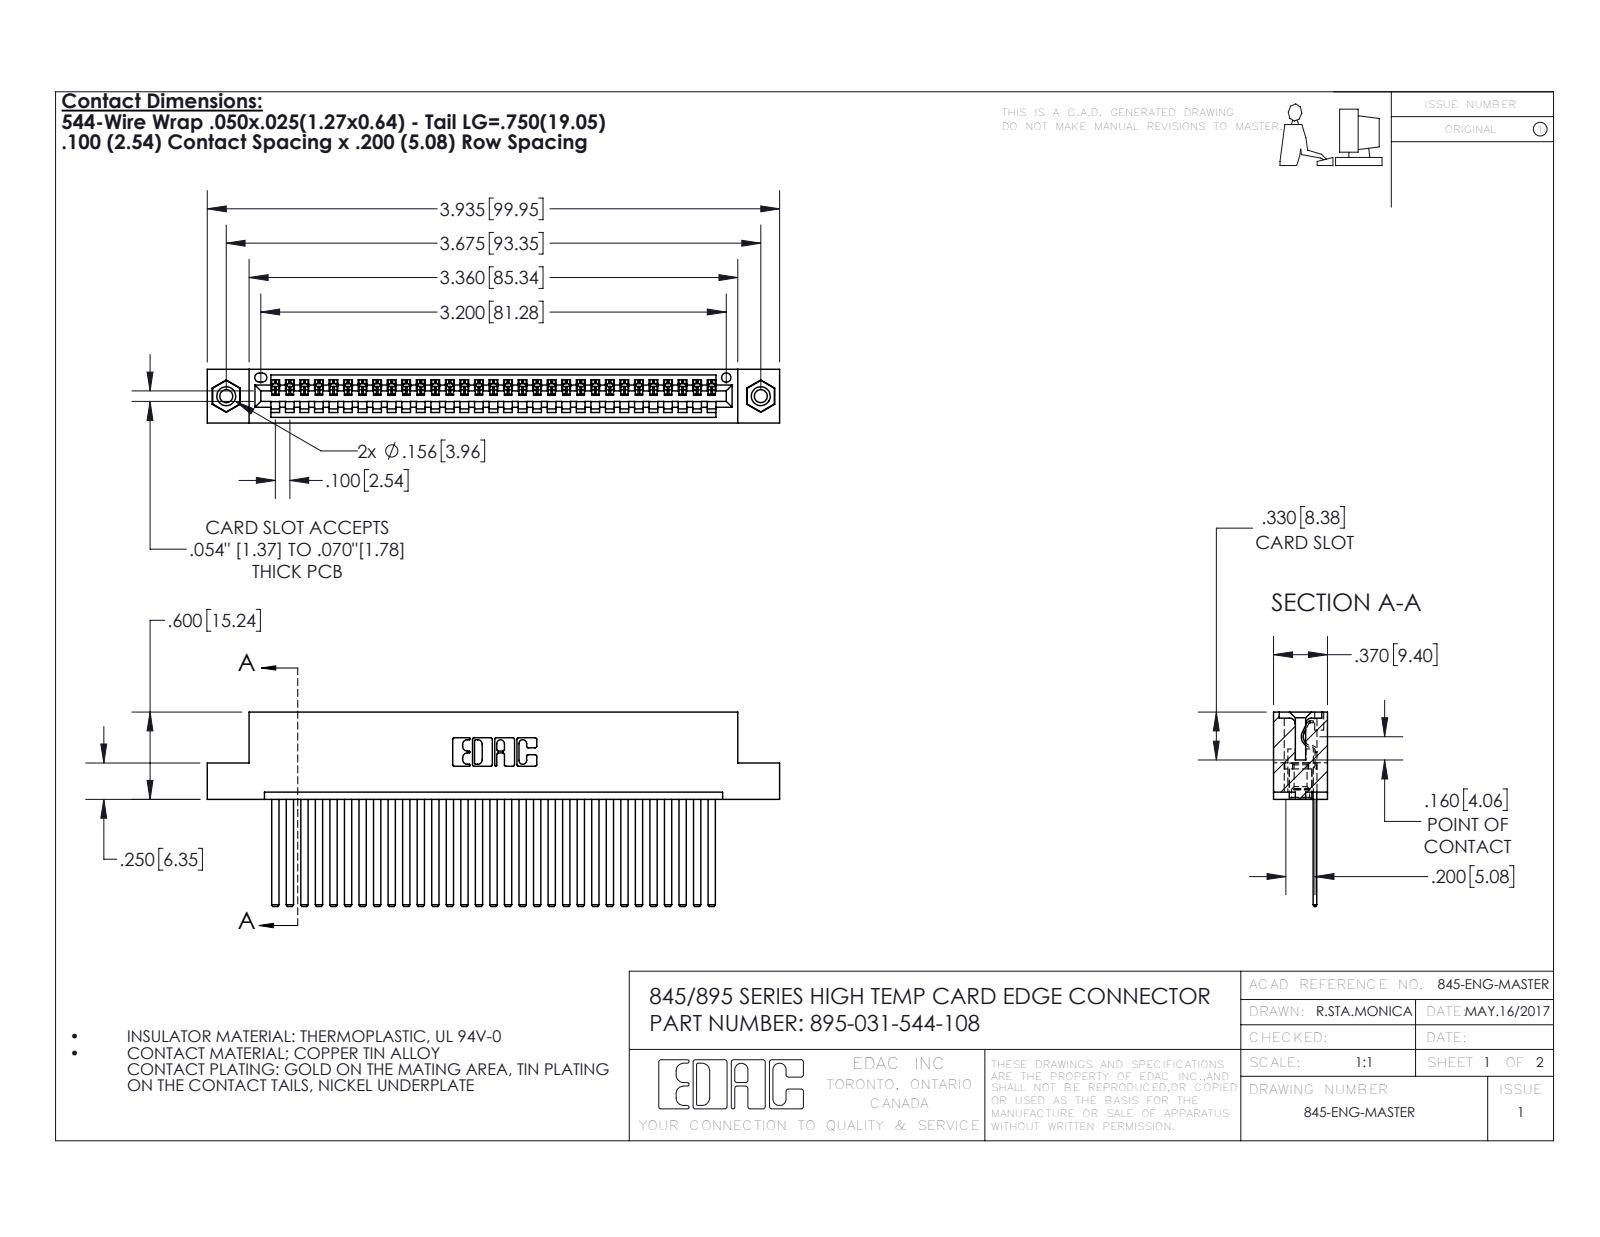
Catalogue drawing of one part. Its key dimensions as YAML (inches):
part_name: "345-250-001_345-250-003-102; 345-292-001_345-293-144; 345 Part_Flush Mounting Lugs - 0.156 Dia-TI; 395-031-544-108"
step_written_by: "SolidWorks 2016 (CONFIG_CONTROL_DESIGN)"
units: inches
bodies: {solids: 34, faces: 1798, planar: 1228, cylindrical: 554, other: 16}
overall_size: [3.935, 1.337, 0.37]
volume: 0.595
surface_area: 21.56
round_holes:
  - {diameter: 0.089, count: 2}
  - {diameter: 0.125, count: 2}
  - {diameter: 0.156, count: 2}
  - {diameter: 0.064, count: 1}
round_bosses_or_shafts:
  - {diameter: 0.155, count: 2}
partial_cylinders:
  - {radius: 0.006, count: 62}
  - {radius: 0.01, count: 22}
  - {radius: 0.007, count: 6}
  - {radius: 0.031, count: 6}
  - {radius: 0.026, count: 3}
  - {radius: 0.031, count: 2}
  - {radius: 0.04, count: 2}
  - {radius: 0.014, count: 1}
face_to_face_distances: [0.072, 0.298, 0.098, 0.025, 0.272, 0.2, 0.37, 0.225, 0.149, 0.072]
hole_center_spacings: [0.27, 3.44, 3.675]
